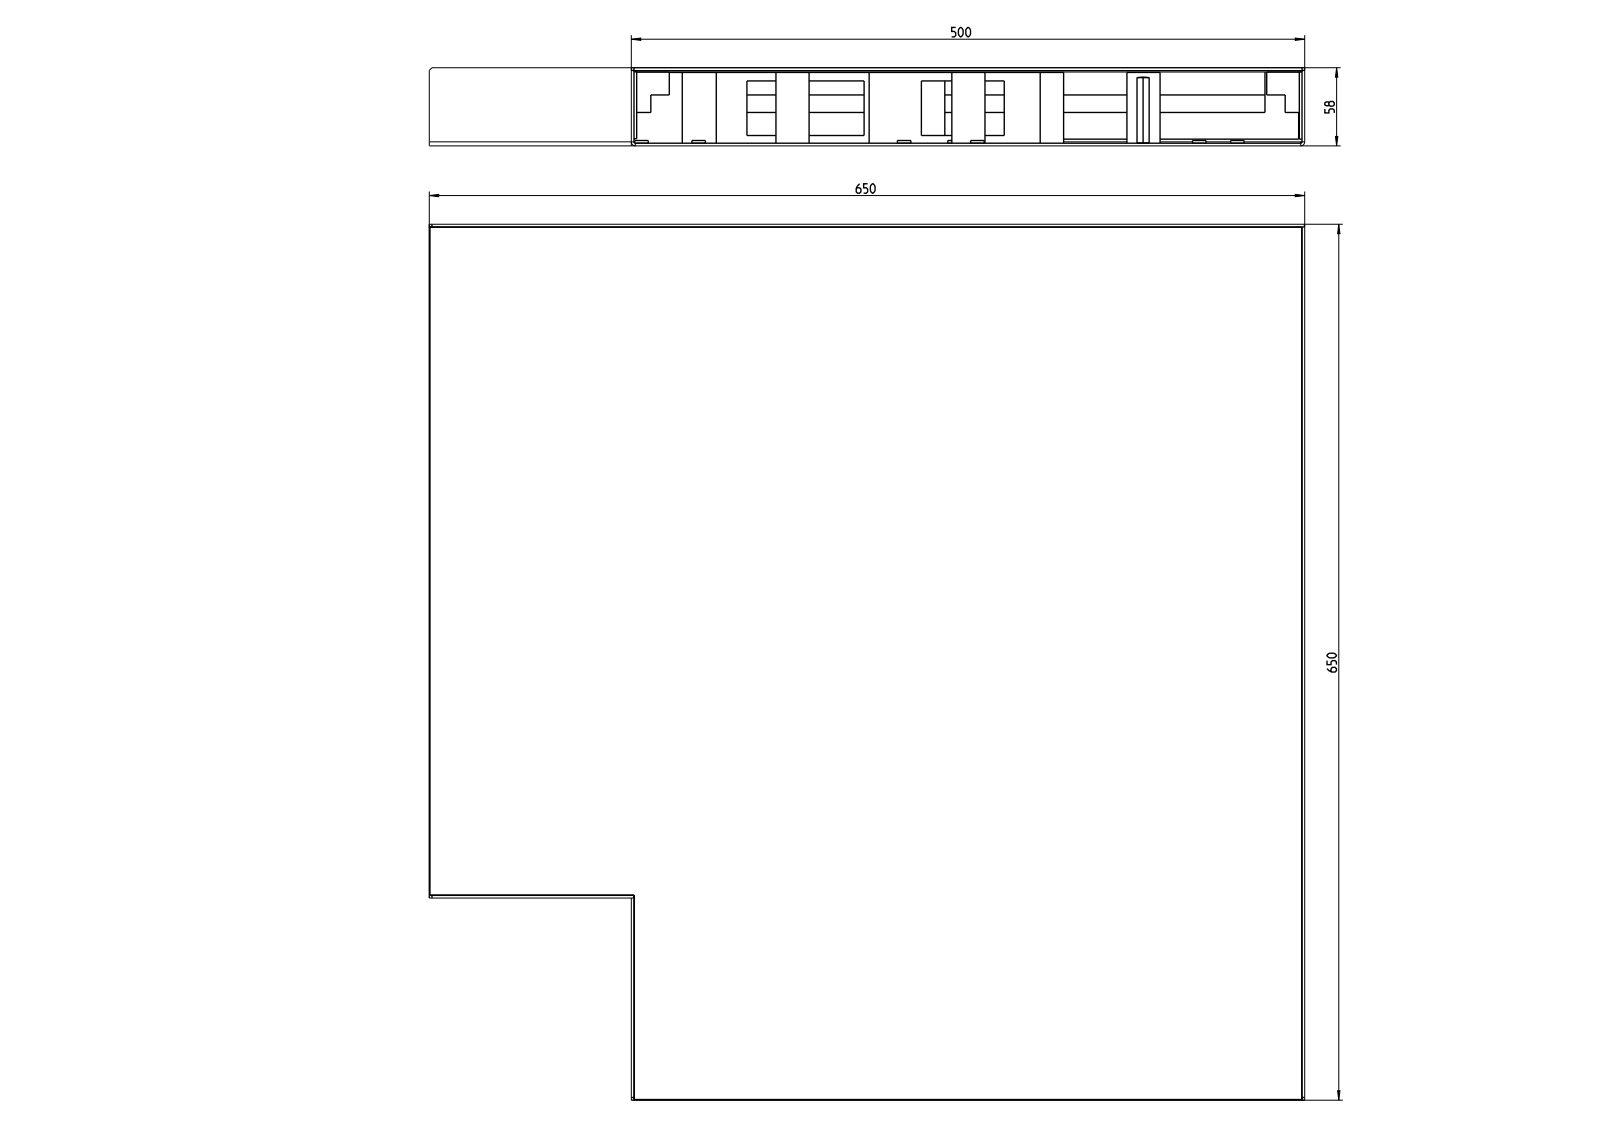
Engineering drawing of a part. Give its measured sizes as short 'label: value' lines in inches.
name: T-01228; T-01221; T-01248; T-01247 (+8 more)
written by: CREO PARAMETRIC BY PTC INC, 2022024 (AUTOMOTIVE_DESIGN)
unit: in
bodies: 18 solids, 456 faces (299 planar, 105 cylindrical, 52 other)
size: 32.038 × 29.728 × 2.293
volume: 223.6 in³; area: 3 833 in²
holes: 12× ⌀0.236, 8× ⌀0.256, 7× ⌀0.535
bosses: 12× ⌀0.394
rounds: 4× R0.004, 4× R0.039, 4× R0.118
face distances: 0.079, 2.079, 0.039, 2.118, 2.157, 2.197, 0.157, 5.118, 19.528, 4.811
hole spacings: 0.787, 15.748, 3.841, 15.768, 16.21, 1.299, 2.087, 2.972
